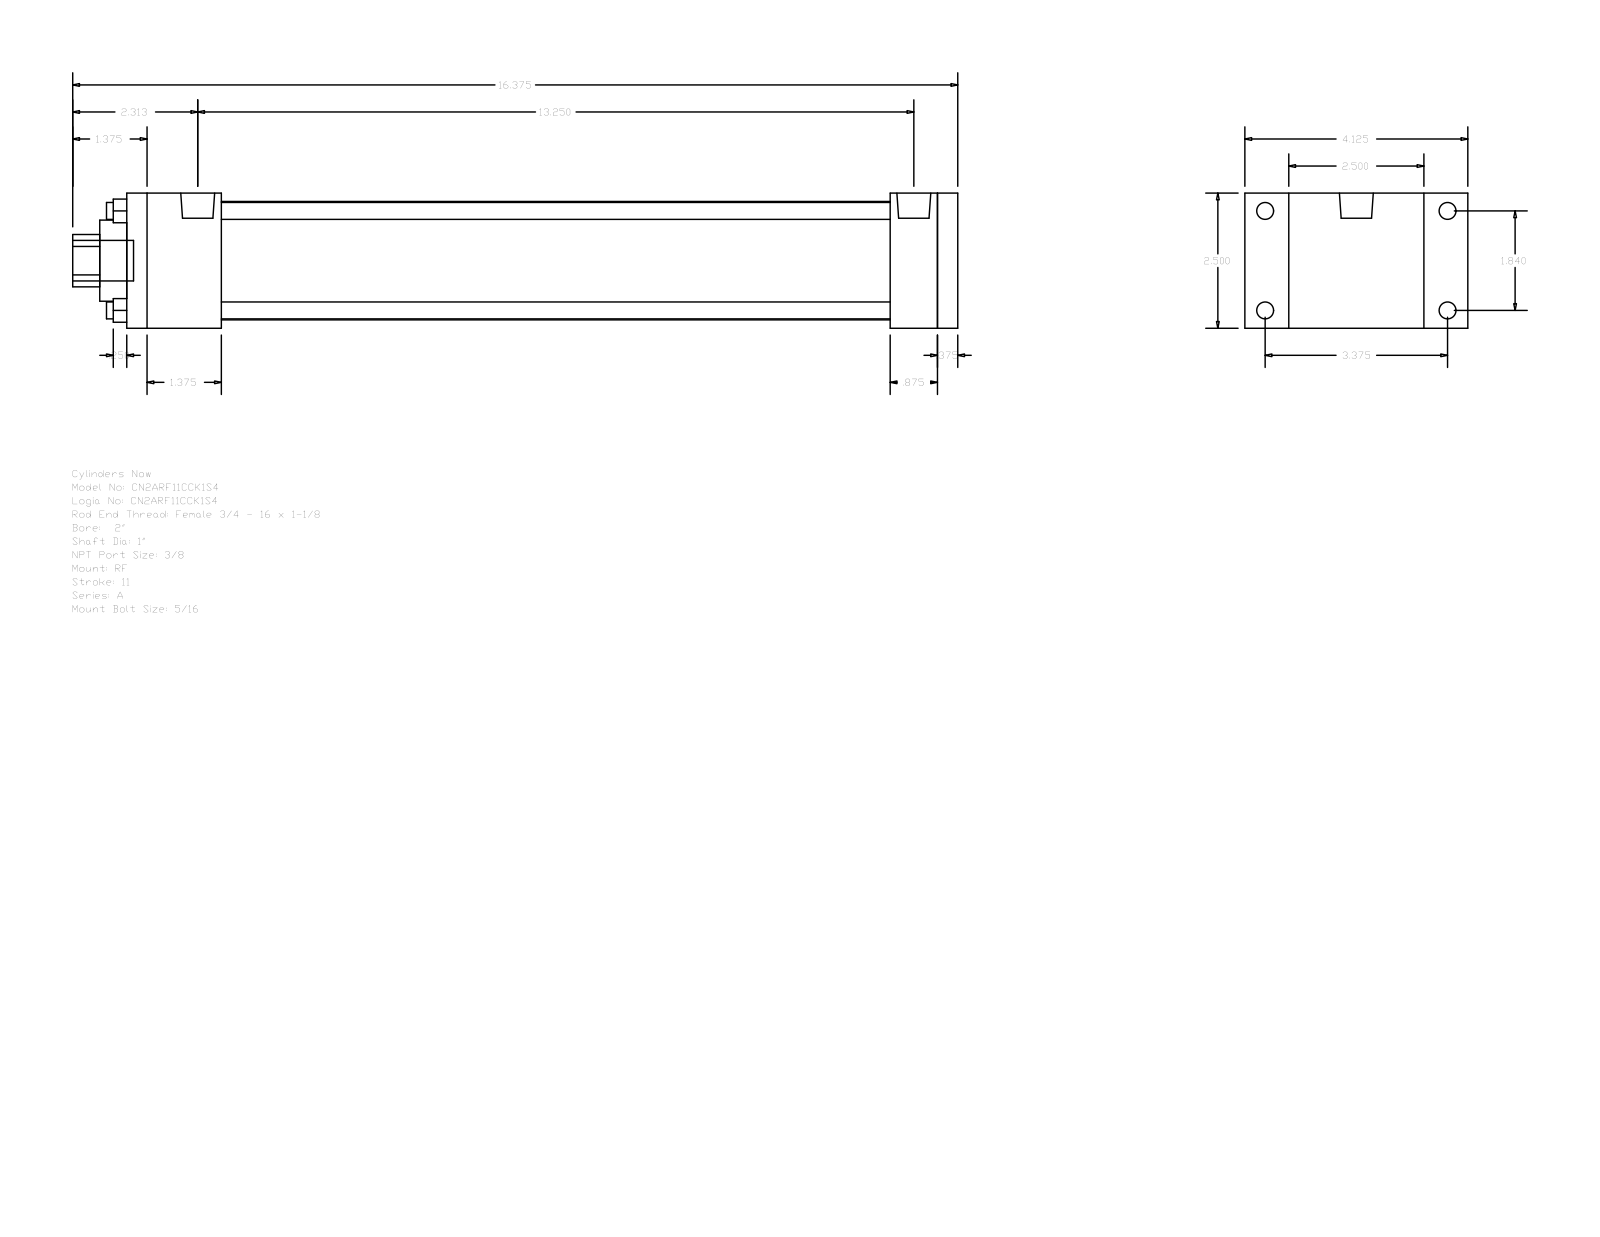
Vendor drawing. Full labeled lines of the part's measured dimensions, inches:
Part name (STEP PRODUCT): A_RF__0200_1
STEP written by: GSSL Pune (CONFIG_CONTROL_DESIGN)
Units: inches
Bodies: 0 solids, 92 faces (64 planar, 28 cylindrical, 0 other)
Overall size (bounding box): 16.375 × 4.125 × 2.5
Round holes (diameter × count): ⌀0.313 ×4, ⌀1 ×1, ⌀1.5 ×1, ⌀2.19 ×1
Round bosses / shafts (diameter × count): ⌀0.313 ×4, ⌀0.219 ×4, ⌀0.627 ×2, ⌀0.75 ×1
Partial cylindrical surfaces — rounded edges, fillets, slot ends (radius × count): R0.484 ×1
Main face-to-face distances: 2.5, 0.375, 15.375, 15, 0.813, 1.75, 13.25, 13.625, 14.125, 12.375
Hole centre spacings: 1.301, 1.84, 2.602
